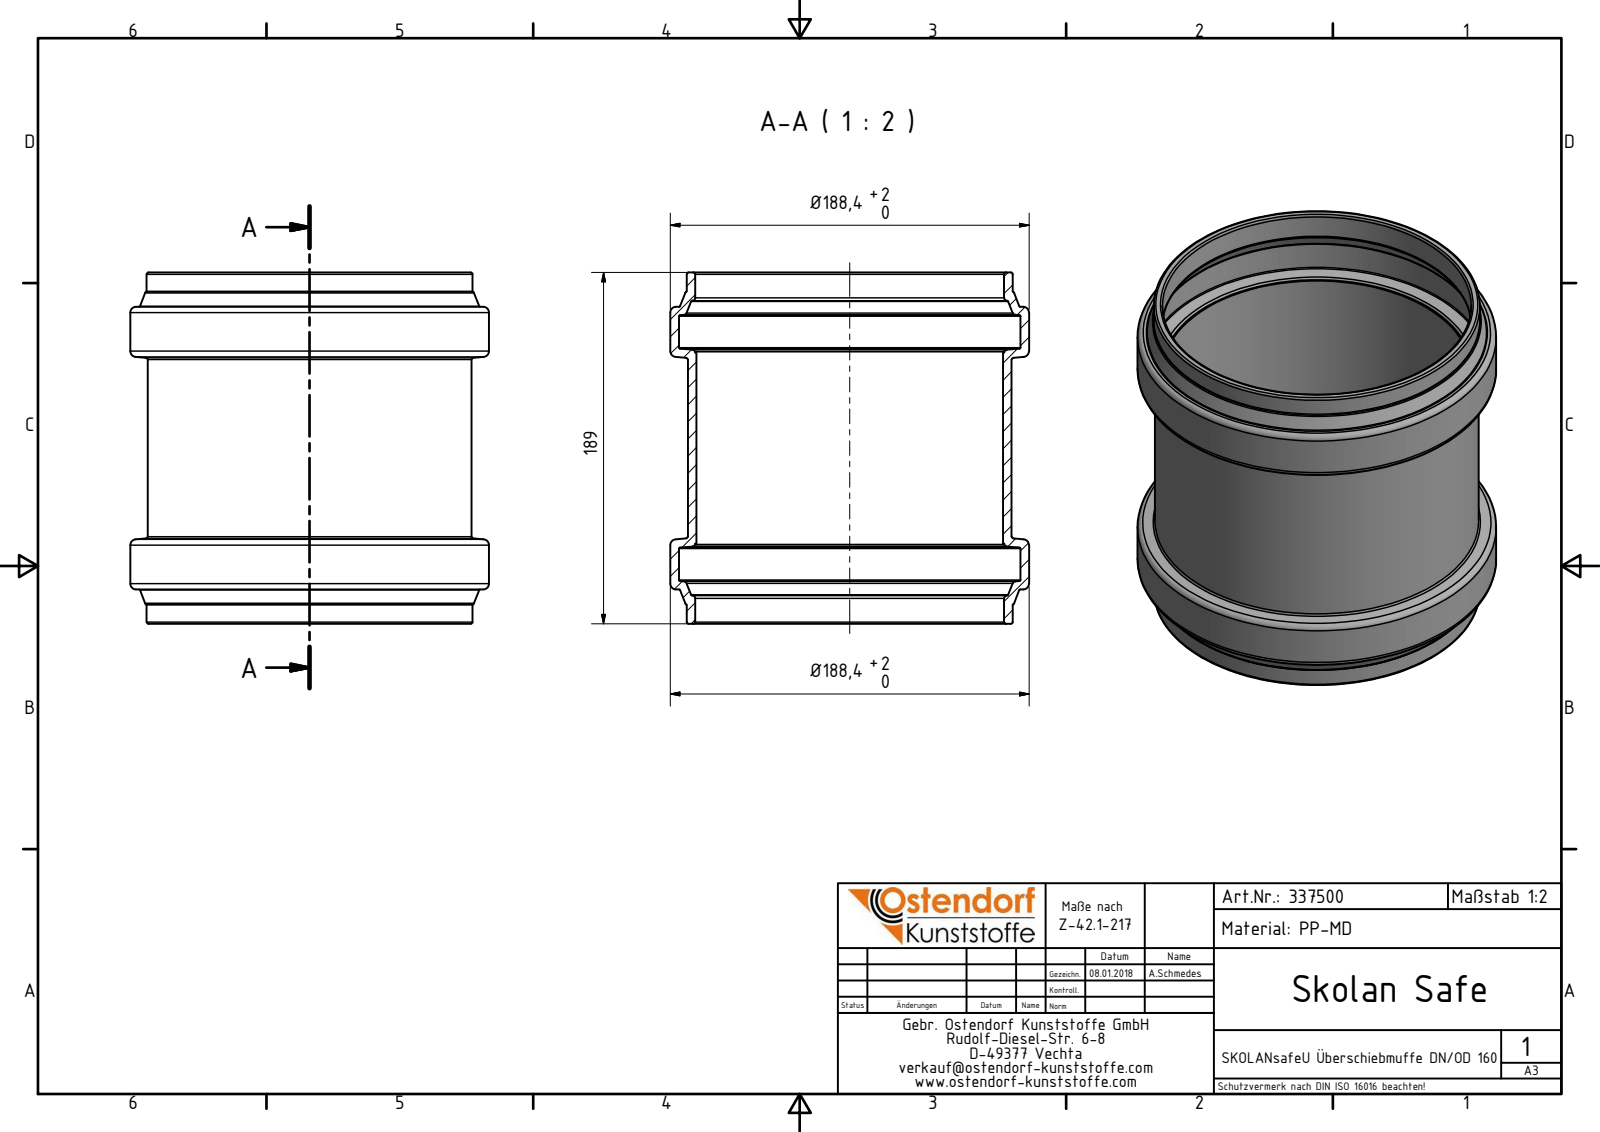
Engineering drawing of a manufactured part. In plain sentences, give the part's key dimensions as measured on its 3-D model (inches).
The part is named "337500 SKOLANsafeU Überschiebmuffe DN_OD 160". Its 3-D file was written by "Autodesk Inventor 2016 (AUTOMOTIVE_DESIGN)". It is 1 solid with 58 faces: 6 planar, 12 cylindrical and 40 other. Overall it measures 7.417 by 7.417 by 7.264 inches. Its volume is 31.17 cubic inches and its surface area 355.3 square inches. Round holes: 1 of diameter 6.339, 1 of diameter 6.386, 1 of diameter 7.063. Round bosses or shafts: 1 of diameter 7.417, 1 of diameter 6.74, 1 of diameter 6.693. The main face-to-face distances are 0.713, 6.551, 7.264, 5.839, 1.636, 5.628, 0.923, 4.915, 3.992.
